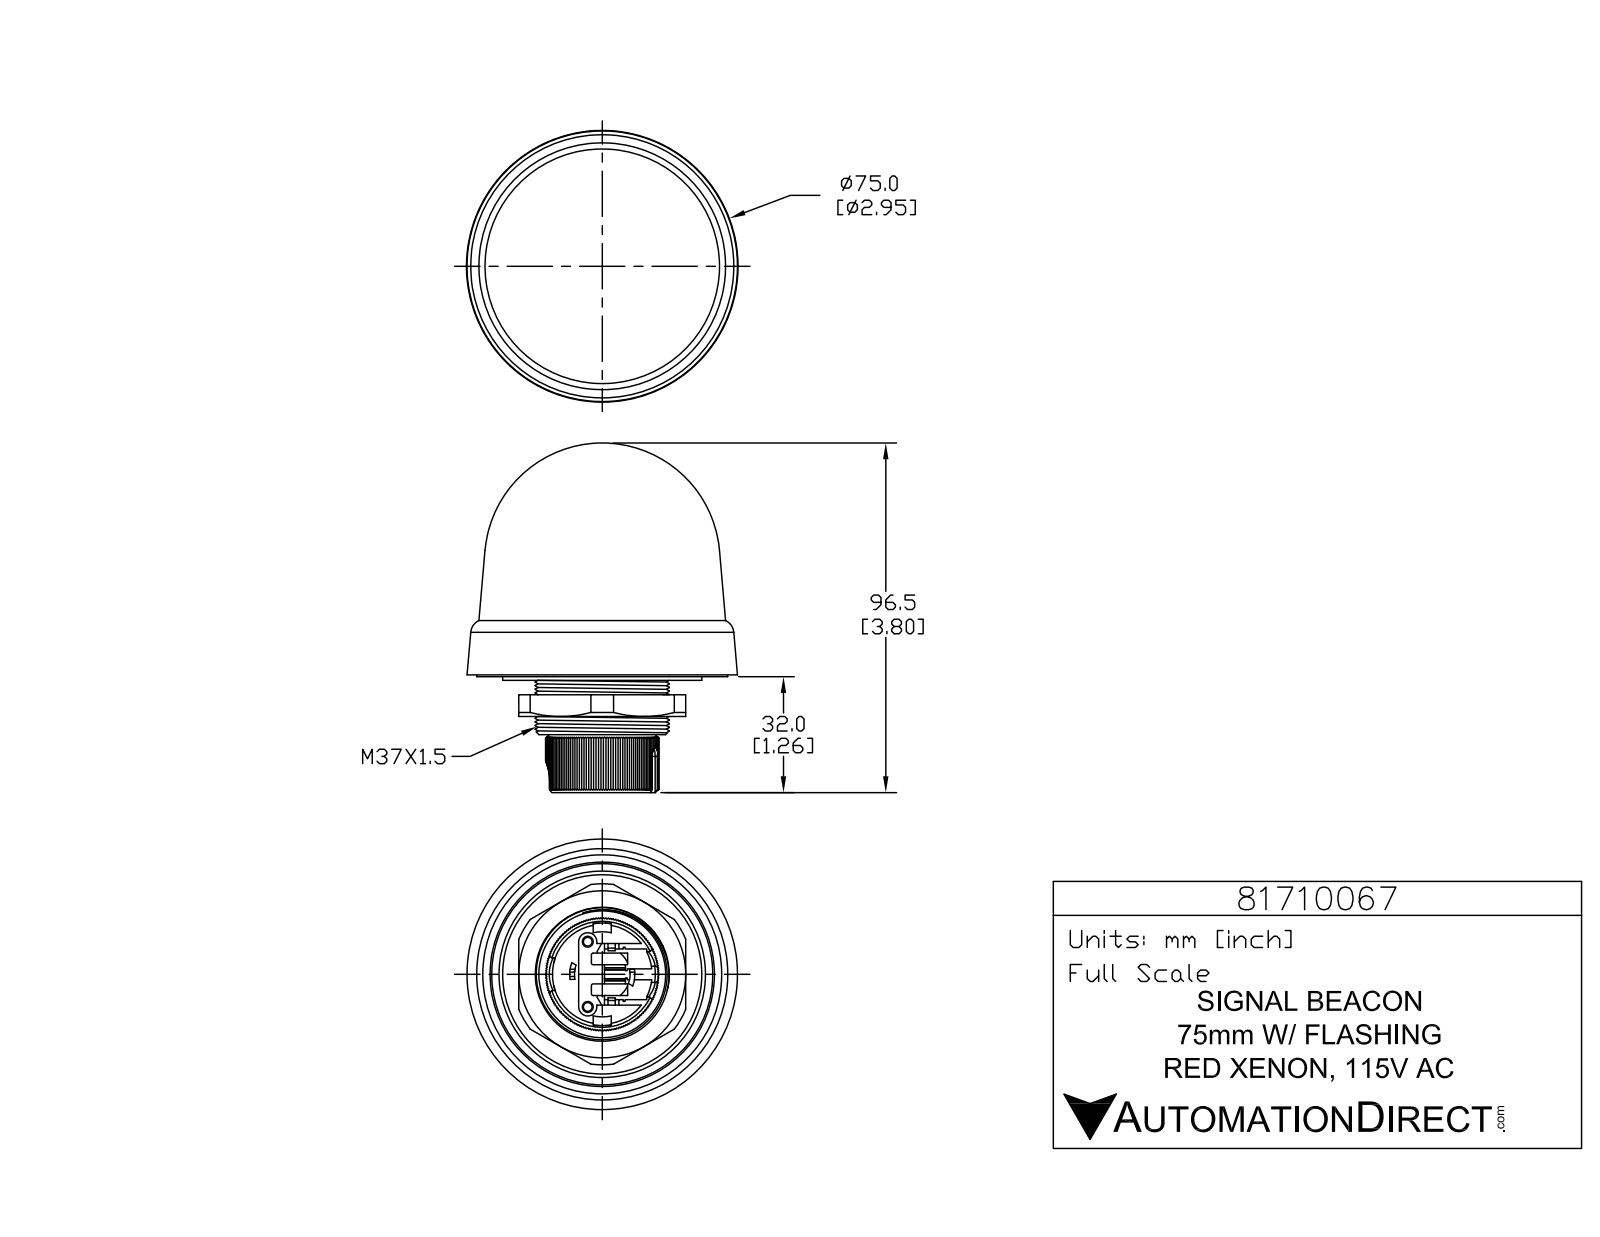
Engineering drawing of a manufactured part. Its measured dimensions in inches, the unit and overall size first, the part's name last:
Units: inches
Overall size (bounding box): 3.799 × 2.941 × 2.941
Round holes (diameter × count): ⌀0.094 ×2, ⌀0.118 ×2, ⌀0.604 ×1, ⌀1.142 ×1
Round bosses / shafts (diameter × count): ⌀0.217 ×2, ⌀0.067 ×2, ⌀2.165 ×1, ⌀1.457 ×1, ⌀0.925 ×1
Partial cylindrical surfaces — rounded edges, fillets, slot ends (radius × count): R0.008 ×6, R0.039 ×6, R0.02 ×4, R0.031 ×2, R0.079 ×2, R0.098 ×2, R0.177 ×1, R0.354 ×1
Main face-to-face distances: 0.177, 0.354, 0.197, 0.433, 0.512, 0.335, 0.059, 0.394, 0.118, 0.157
Hole centre spacings: 0.388, 0.709
Volume: 12.36 in³ · Surface area: 58.68 in²
Bodies: 3 solids, 560 faces (432 planar, 80 cylindrical, 48 other)
Part name (STEP PRODUCT): 81710067
STEP written by: SolidWorks 2019 (CONFIG_CONTROL_DESIGN)
